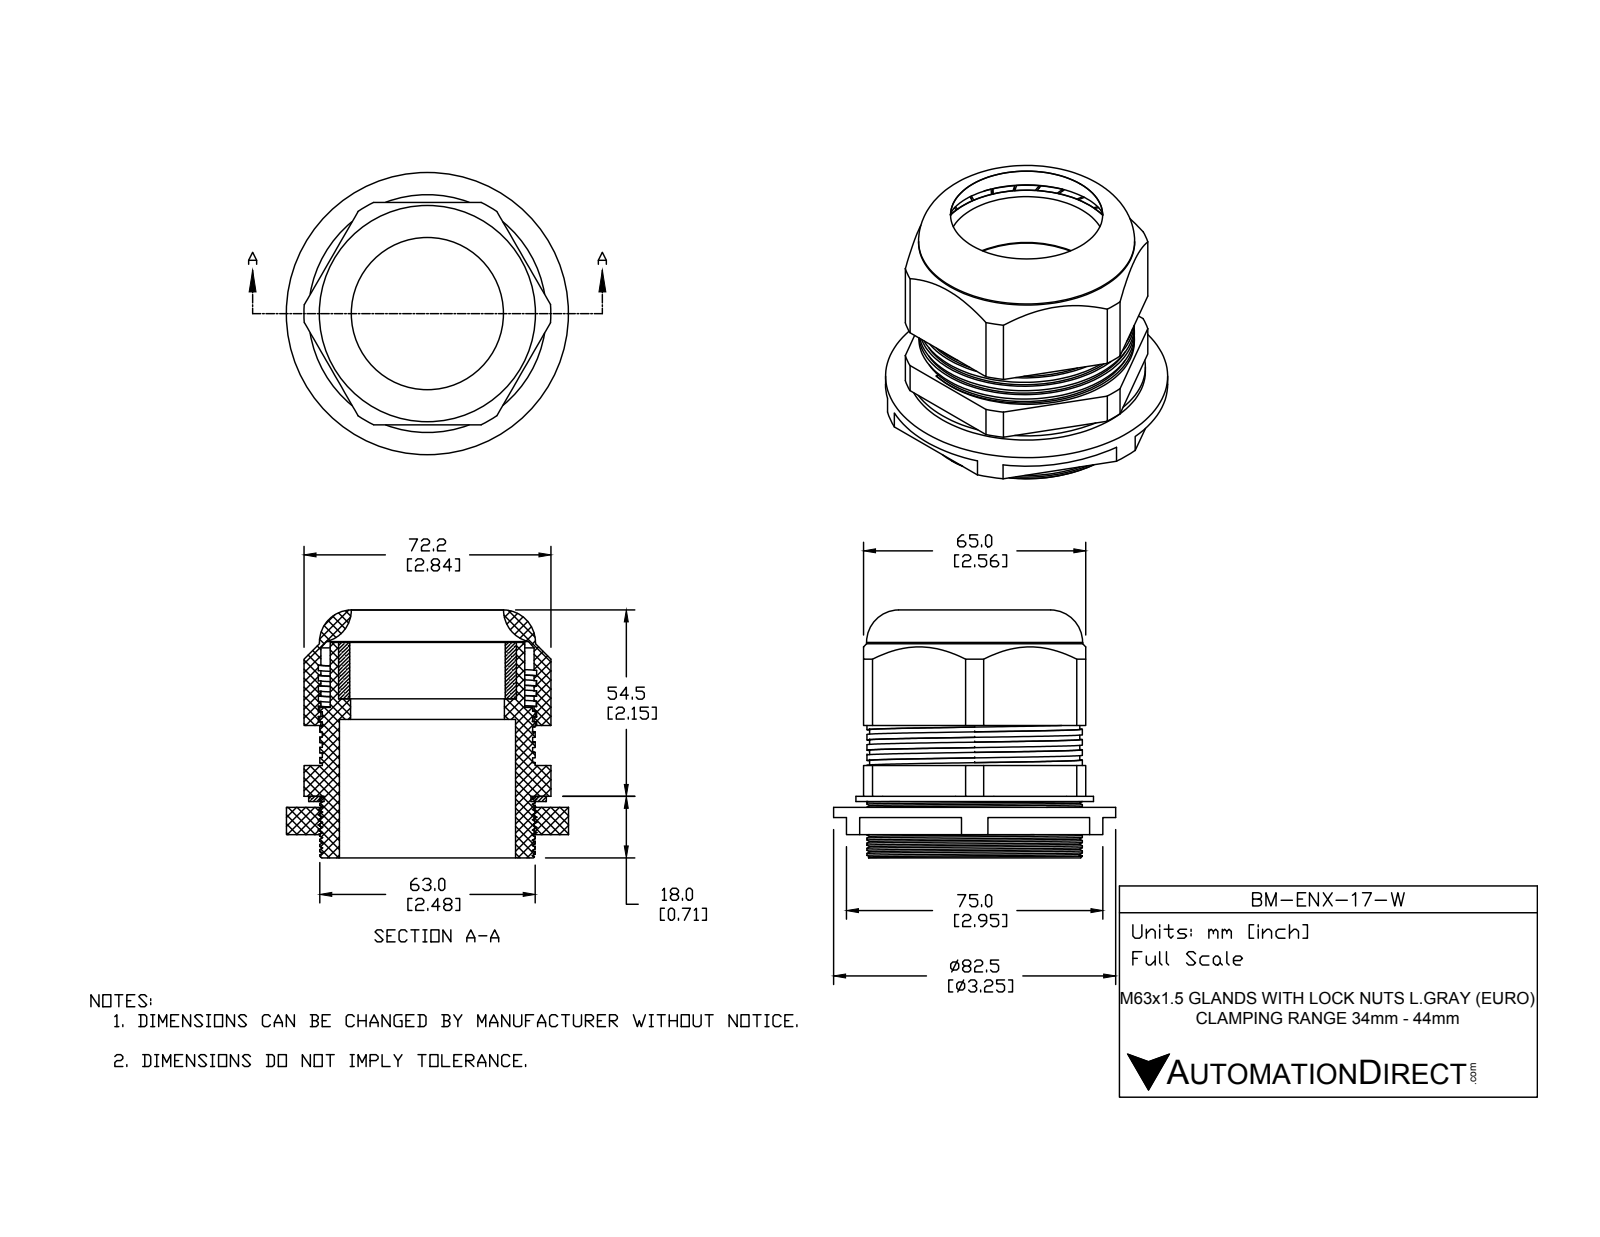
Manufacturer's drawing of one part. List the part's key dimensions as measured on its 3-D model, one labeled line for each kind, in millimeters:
Part name (STEP PRODUCT): BM-ENX-17-W
STEP written by: SolidWorks 2015 (CONFIG_CONTROL_DESIGN)
Units: millimetres
Bodies: 5 solids, 259 faces (139 planar, 99 cylindrical, 21 other)
Overall size (bounding box): 82.5 × 82.5 × 72.5
Volume: 104 139 mm³ · Surface area: 66 732 mm²
Round holes (diameter × count): ⌀44.5 ×1, ⌀45 ×1, ⌀45.5 ×1, ⌀51.5 ×1, ⌀52 ×1, ⌀60.5 ×1, ⌀62.33 ×1
Round bosses / shafts (diameter × count): ⌀82.5 ×1, ⌀69.5 ×1, ⌀63.2 ×1, ⌀63 ×1, ⌀56.9 ×1
Partial cylindrical surfaces — rounded edges, fillets, slot ends (radius × count): R36.1 ×1
Main face-to-face distances: 65, 46.5, 16.5, 8, 5, 11.2, 3.2, 70, 39.7, 31.7
